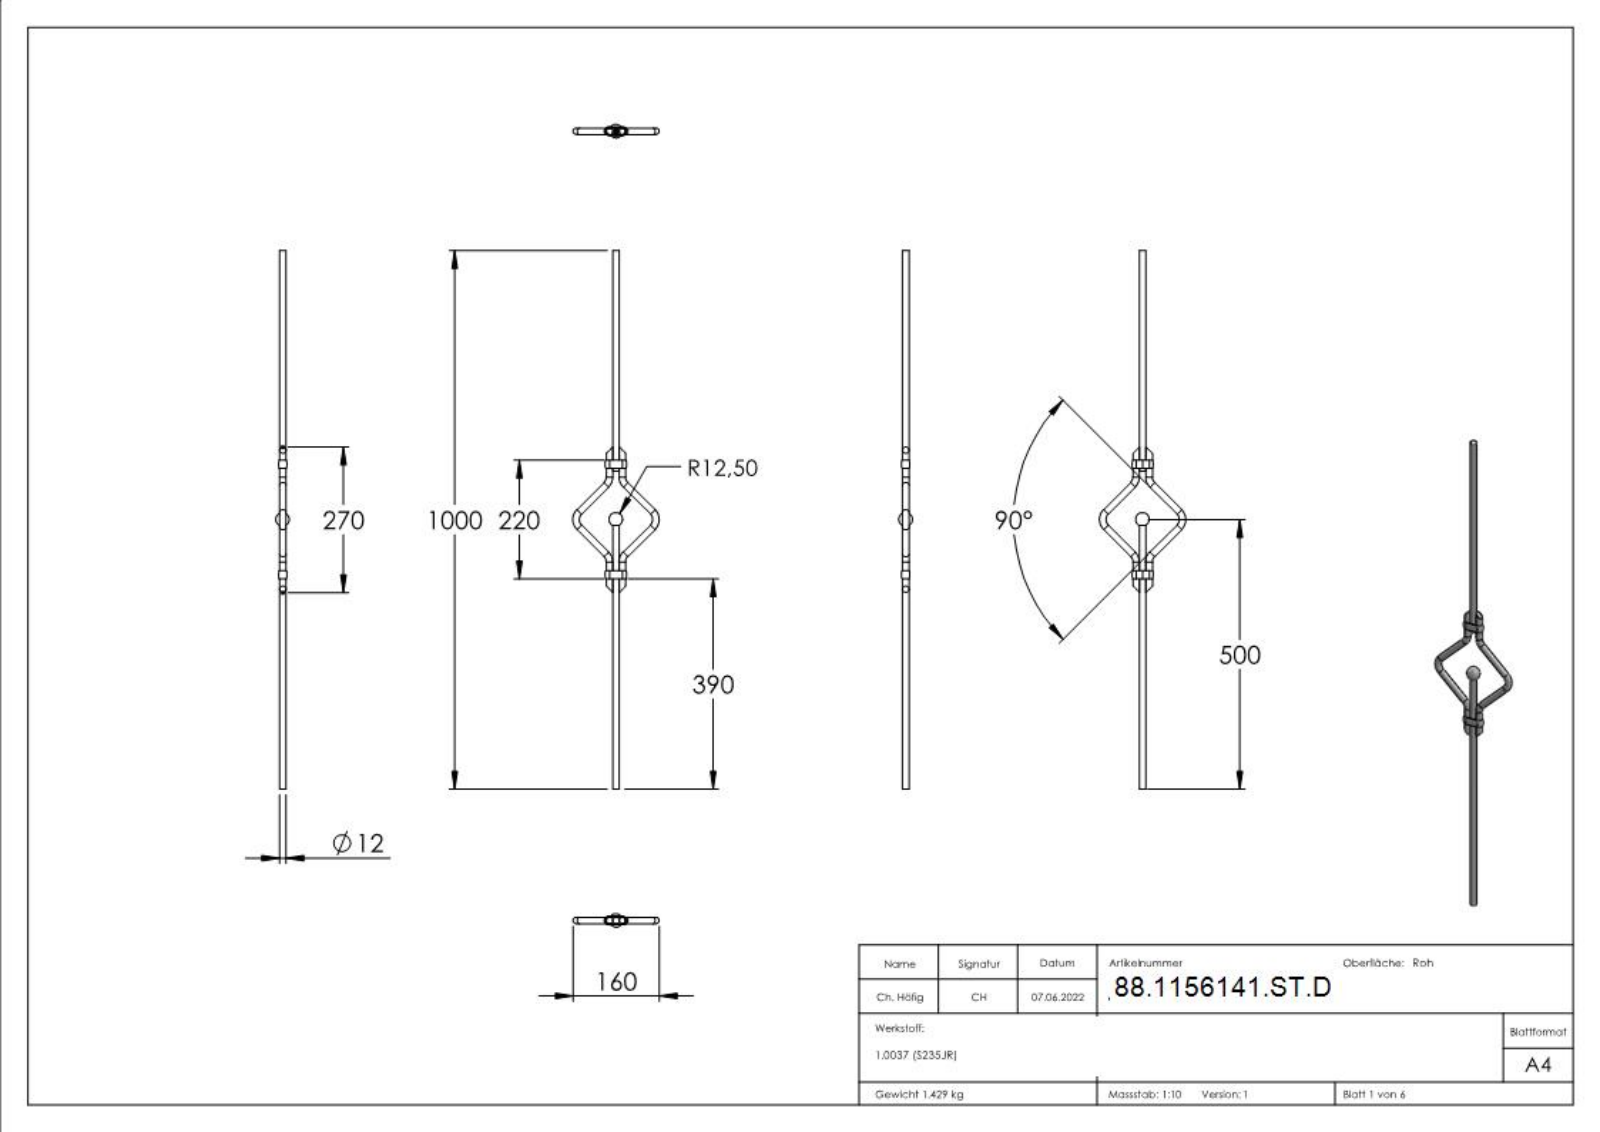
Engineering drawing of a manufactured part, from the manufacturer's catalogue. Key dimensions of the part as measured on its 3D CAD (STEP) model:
Part name (STEP PRODUCT): 56141-ST-D Teil2_56141-ST-D Teil2; 56141-ST-D; 56141-ST-D Teil4_56141-ST-D Teil4; 56141-ST-D Teil1_56141-ST-D Teil1 (+1 more)
STEP written by: SolidWorks 2018 (CONFIG_CONTROL_DESIGN)
Units: millimetres
Bodies: 6 solids, 330 faces (192 planar, 20 cylindrical, 118 other)
Overall size (bounding box): 1000 × 160 × 25
Volume: 183 136 mm³ · Surface area: 65 542 mm²
Round bosses / shafts (diameter × count): ⌀12 ×7
Partial cylindrical surfaces — rounded edges, fillets, slot ends (radius × count): R19.5 ×4, R6.2 ×2
Main face-to-face distances: 12.4, 199.38, 410, 590, 1000, 390, 405, 595, 610, 205
